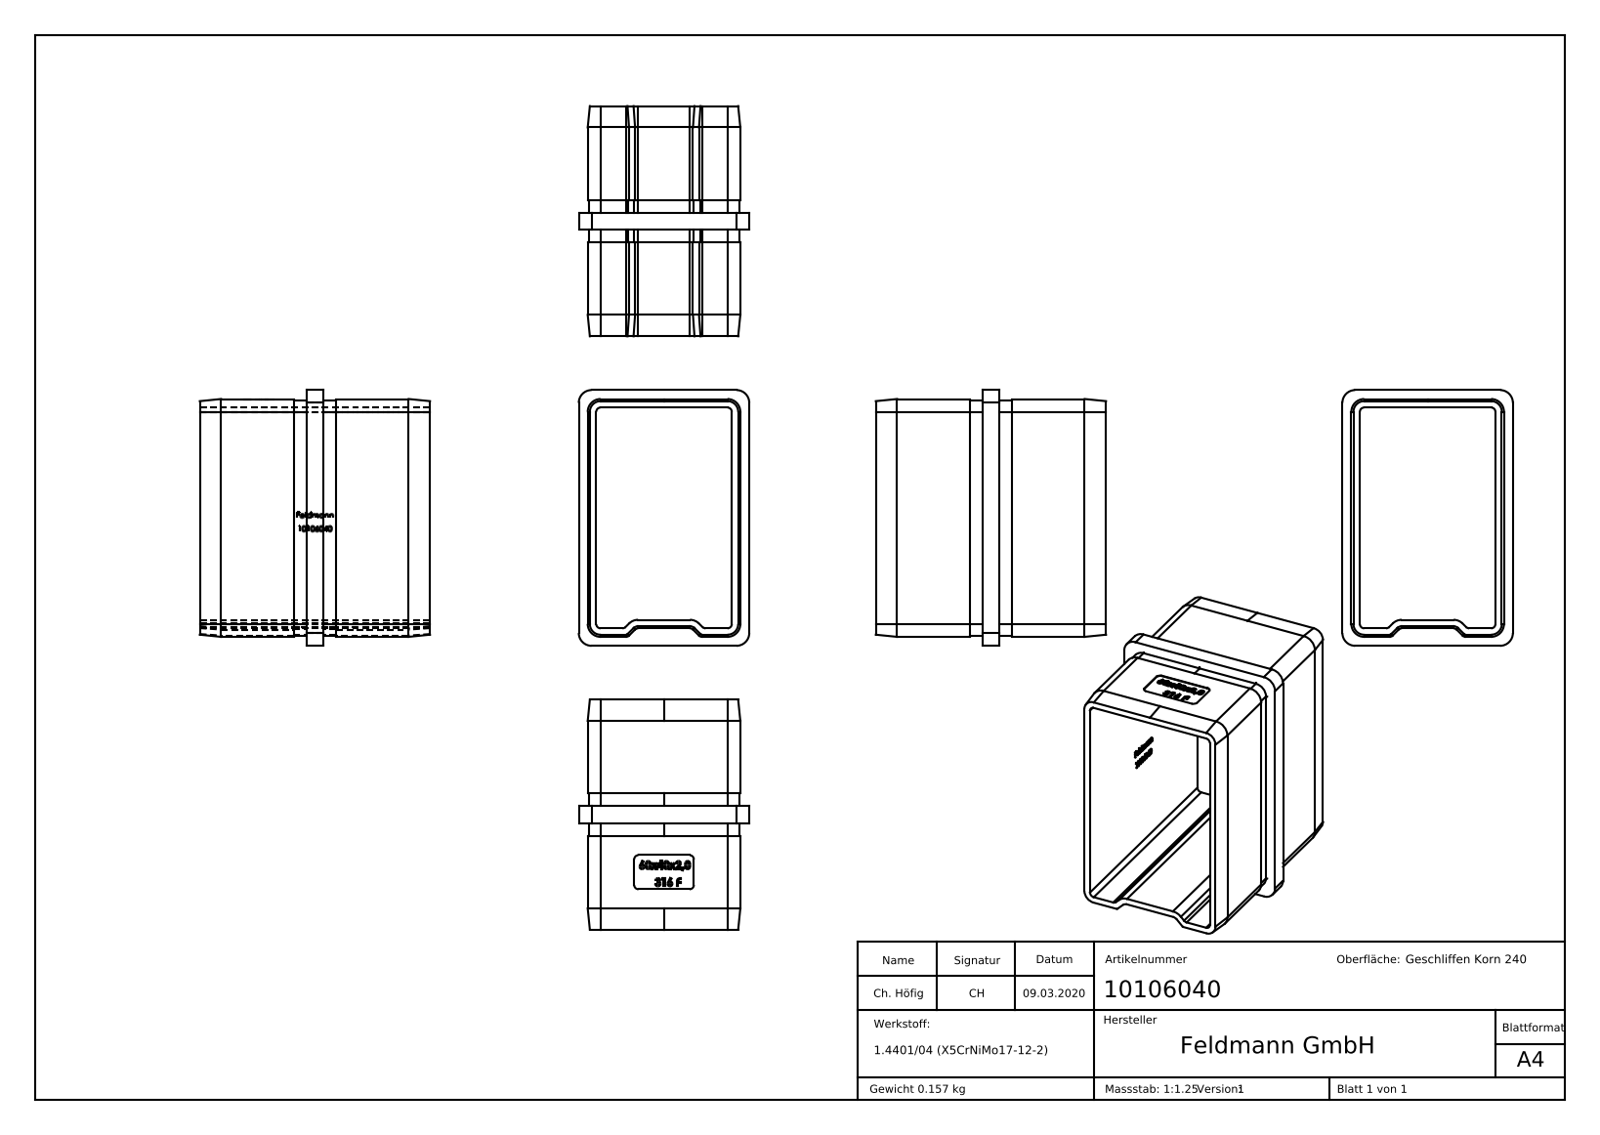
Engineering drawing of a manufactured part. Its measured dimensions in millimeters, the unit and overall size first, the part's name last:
Units: millimetres
Overall size (bounding box): 60 × 54 × 40
Partial cylindrical surfaces — rounded edges, fillets, slot ends (radius × count): R1 ×14, R3 ×10, R2.7 ×4, R0.7 ×2, R1.3 ×2
Main face-to-face distances: 2, 33.8, 31.8, 35.8, 51.8, 53.8, 1.7, 4, 2.1, 4.1
Volume: 19 660 mm³ · Surface area: 20 361 mm²
Bodies: 1 solid, 531 faces (307 planar, 48 cylindrical, 176 other)
Part name (STEP PRODUCT): 10106040
STEP written by: SolidWorks 2015 (CONFIG_CONTROL_DESIGN)
